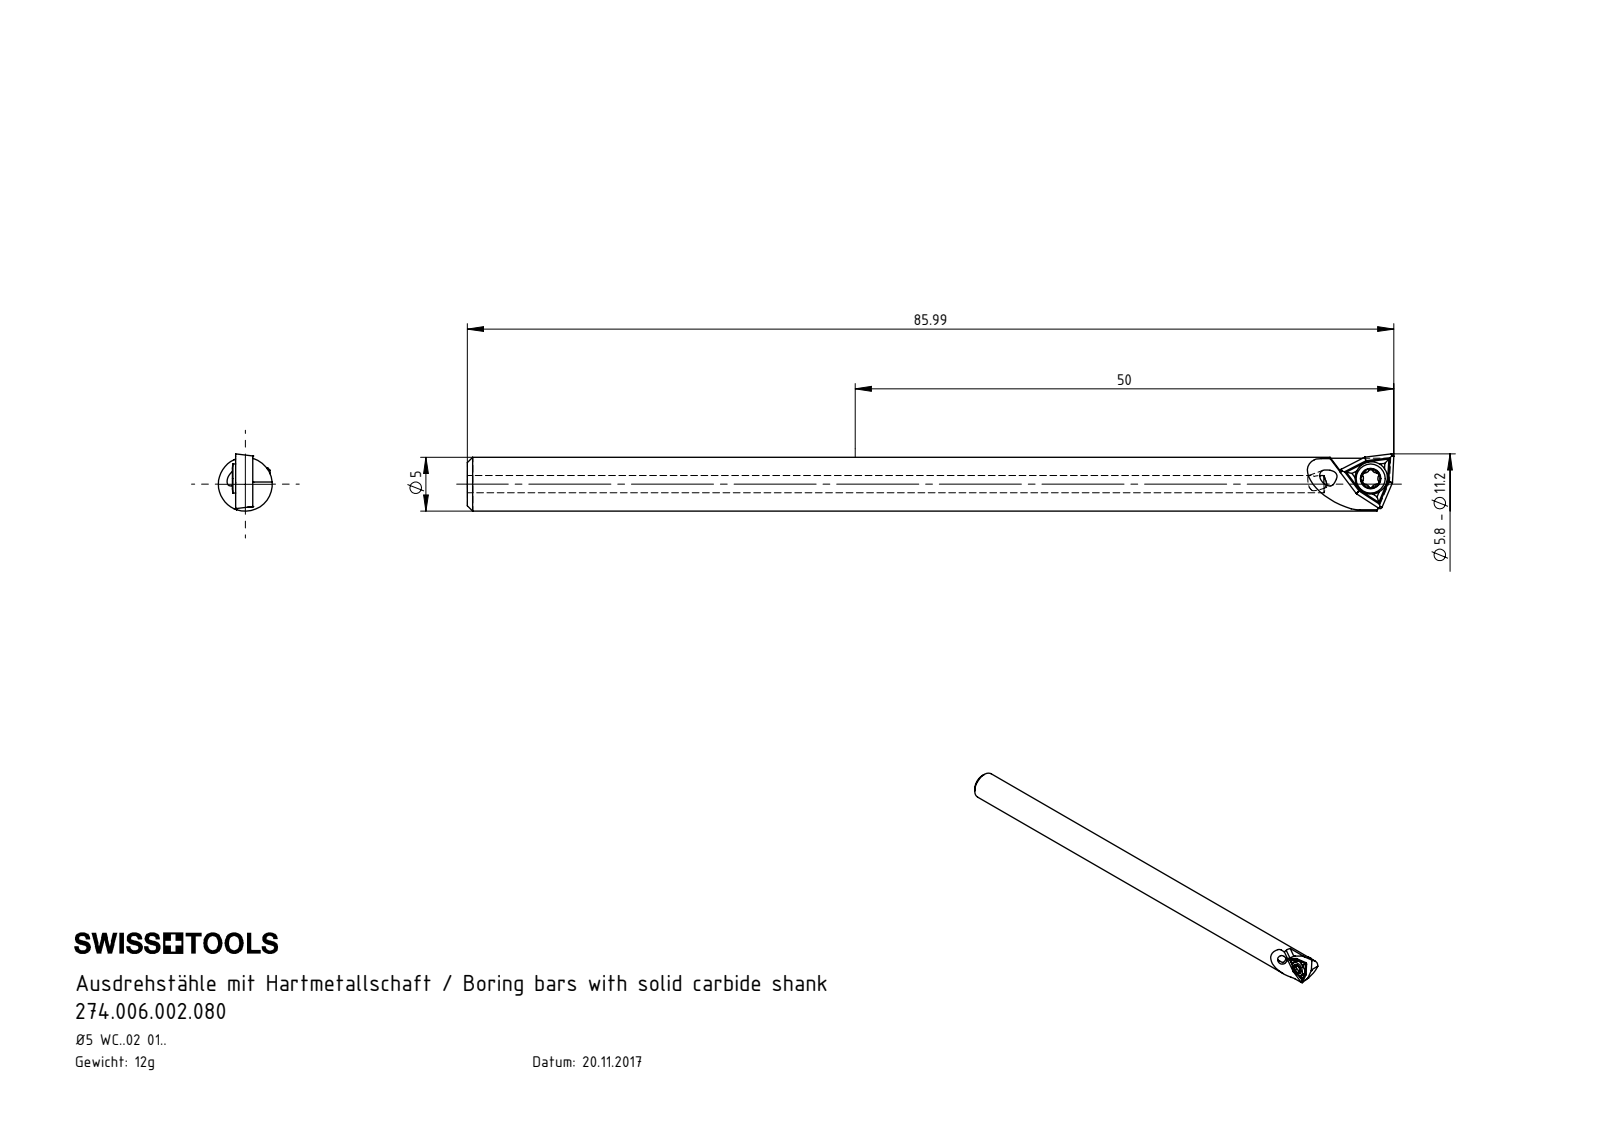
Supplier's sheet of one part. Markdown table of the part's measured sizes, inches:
| quantity | value |
| --- | --- |
| part name | SFS-Torx-M2; WCMT020102; B06-WWA.K11.080_A; 274.006.002.080 |
| STEP written by | SolidWorks 2017 (CONFIG_CONTROL_DESIGN) |
| units | inches |
| bodies | 3 solids, 106 faces (36 planar, 33 cylindrical, 37 other) |
| overall size | 3.385 × 0.209 × 0.197 |
| volume | 0.09 in³ |
| surface area | 2.874 in² |
| round holes (diameter × count) | 0.063 × 3, 0.091 × 1, 0.118 × 1 |
| round bosses / shafts (diameter × count) | 0.197 × 1, 0.106 × 1, 0.079 × 1 |
| partial cylindrical surfaces (radius × count) | 0.008 × 6, 0.014 × 6, 0.031 × 1 |
| main face-to-face distances | 0.059, 0.055, 0.063, 0.118, 0.122, 0.126, 0.063, 0.138, 0.074, 0.02 |
